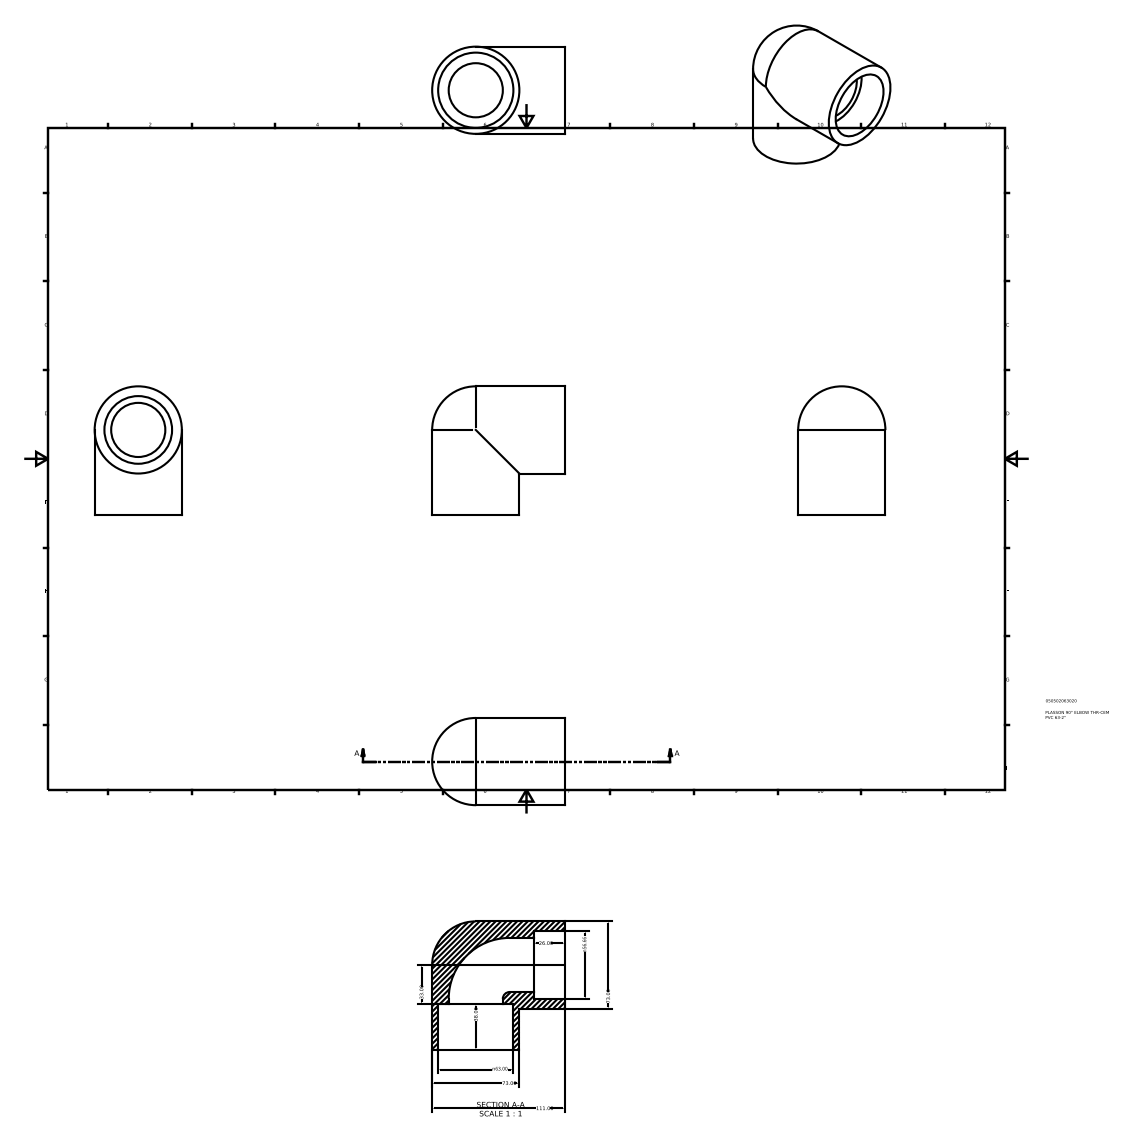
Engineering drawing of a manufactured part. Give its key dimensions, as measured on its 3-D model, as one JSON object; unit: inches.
{"part_name": "050502063020", "step_written_by": "Autodesk Inventor 2015 (AUTOMOTIVE_DESIGN)", "units": "inches", "bodies": {"solids": 1, "faces": 12, "planar": 4, "cylindrical": 6, "other": 2}, "overall_size": [4.37, 4.232, 2.874], "volume_in3": 18.26, "surface_area_in2": 92.06, "round_holes": [[1.784, 2], [2.231, 1], [2.48, 1]], "round_bosses_or_shafts": [[2.874, 2]], "face_to_face_distances": [1.496, 1.024]}
